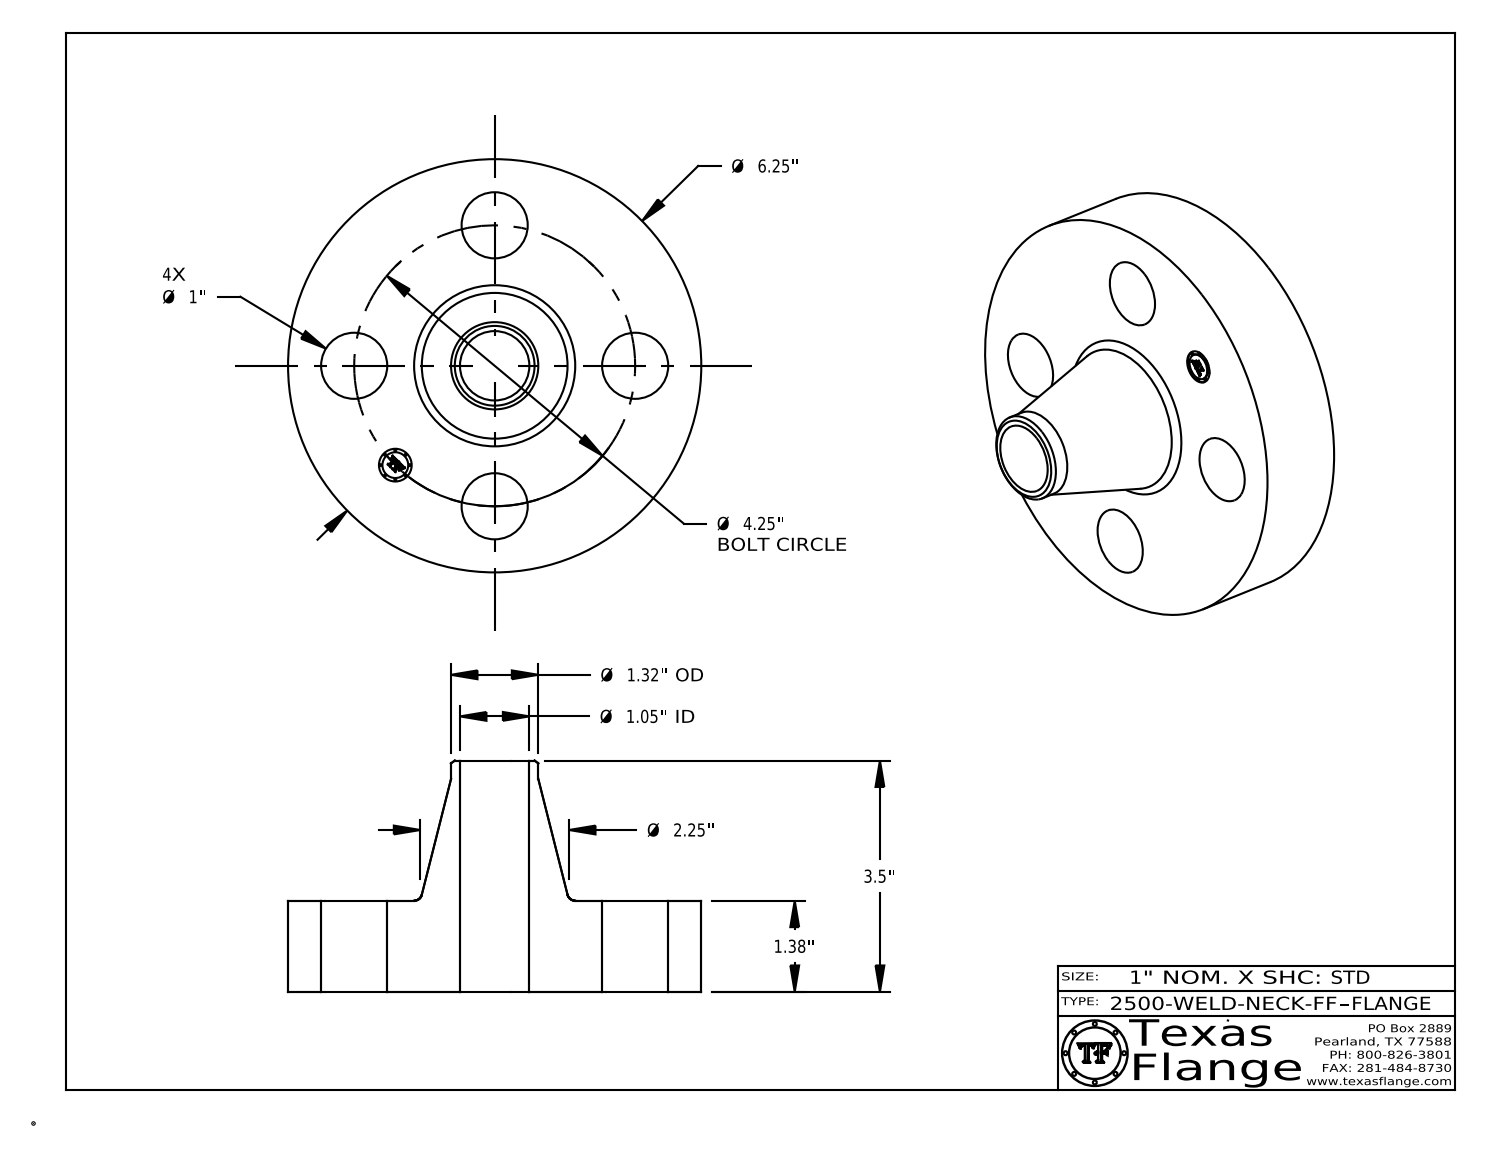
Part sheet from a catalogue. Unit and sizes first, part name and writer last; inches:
Units: inches
Overall size (bounding box): 6.25 × 6.25 × 3.5
Round holes (diameter × count): ⌀1 ×4, ⌀0.495 ×1, ⌀1.049 ×1
Round bosses / shafts (diameter × count): ⌀0.03 ×8, ⌀6.25 ×1, ⌀1.32 ×1, ⌀0.39 ×1
Main face-to-face distances: 1.38, 3.5, 2.12, 1.365, 0.015, 2.135, 0.148, 0.144, 0.027, 0.096
Hole centre spacings: 2.125, 3.006, 1.626, 3.927, 4.25
Volume: 40.08 in³ · Surface area: 118.3 in²
Bodies: 1 solid, 408 faces (368 planar, 34 cylindrical, 6 other)
Part name (STEP PRODUCT): 2500-WELD-NECK-FF
STEP written by: CATIA V5 STEP AP214 (AUTOMOTIVE_DESIGN)
